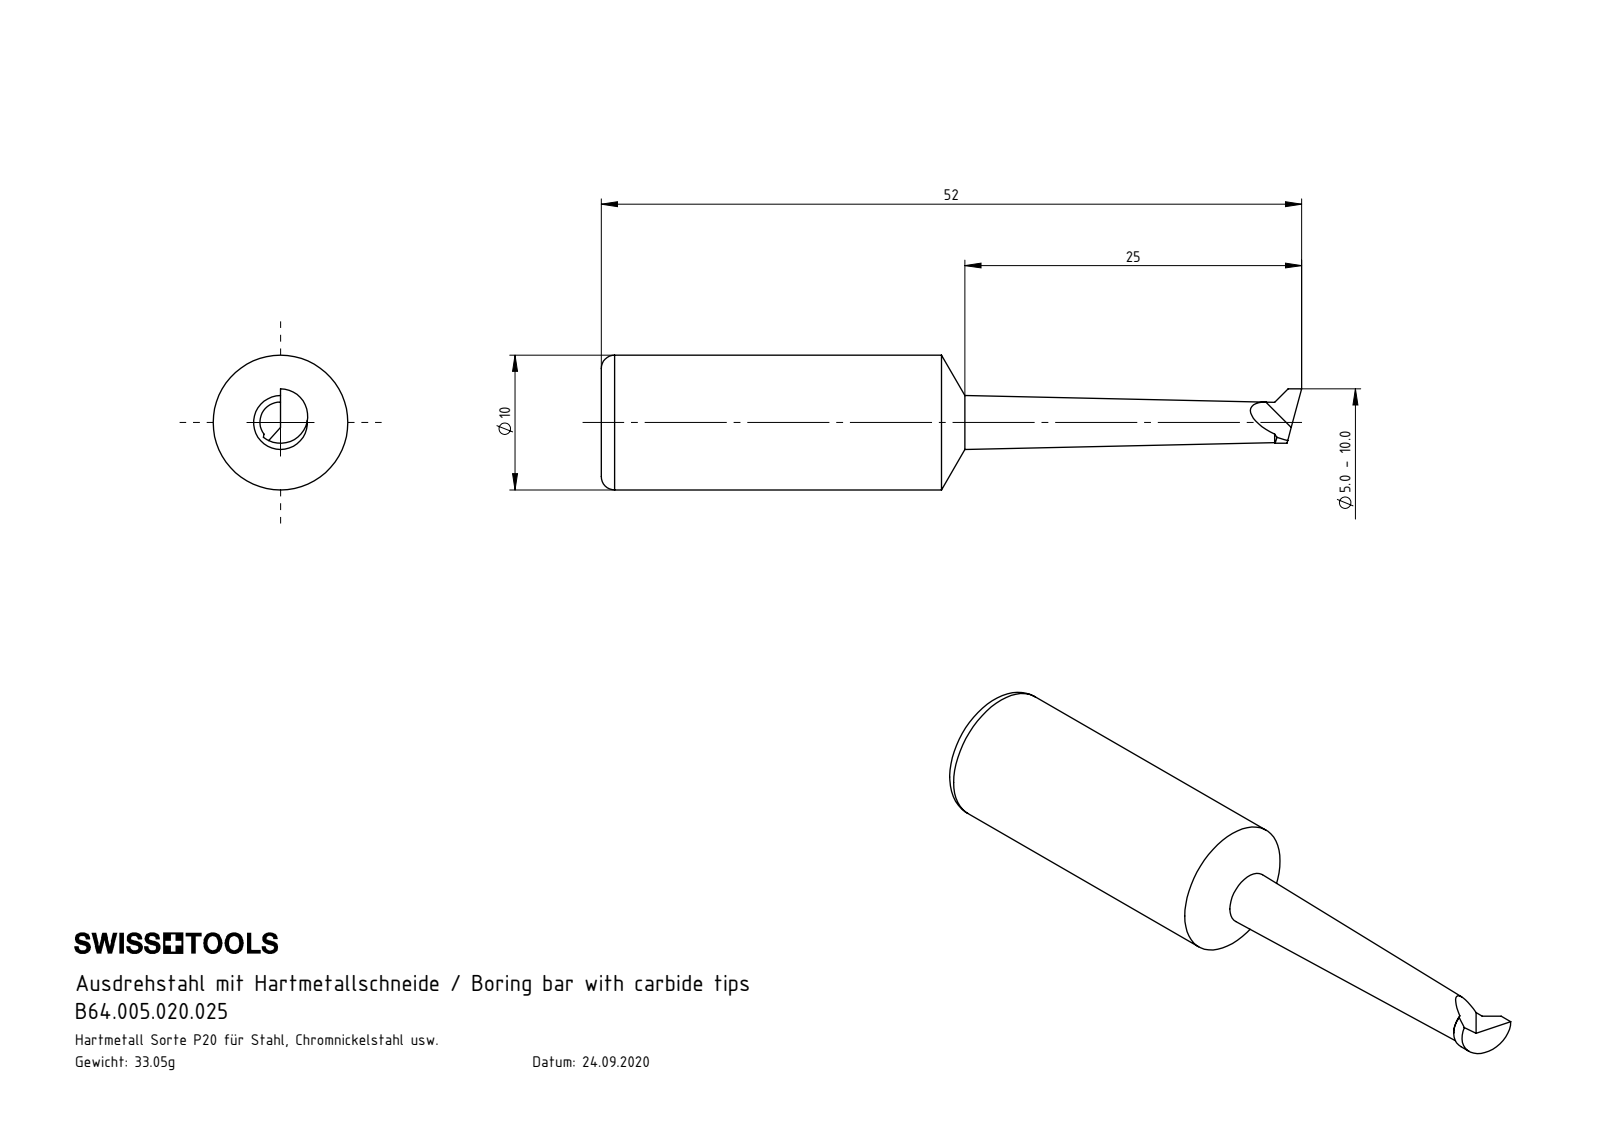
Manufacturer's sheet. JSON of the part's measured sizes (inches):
{"part_name": "B64.005.020.025", "step_written_by": "SolidWorks 2022 (CONFIG_CONTROL_DESIGN)", "units": "inches", "bodies": {"solids": 1, "faces": 14, "planar": 4, "cylindrical": 3, "other": 7}, "overall_size": [2.047, 0.394, 0.394], "volume_in3": 0.139, "surface_area_in2": 1.879, "round_bosses_or_shafts": [[0.394, 1]], "partial_cylinders_radius": [[0.08, 1]]}
